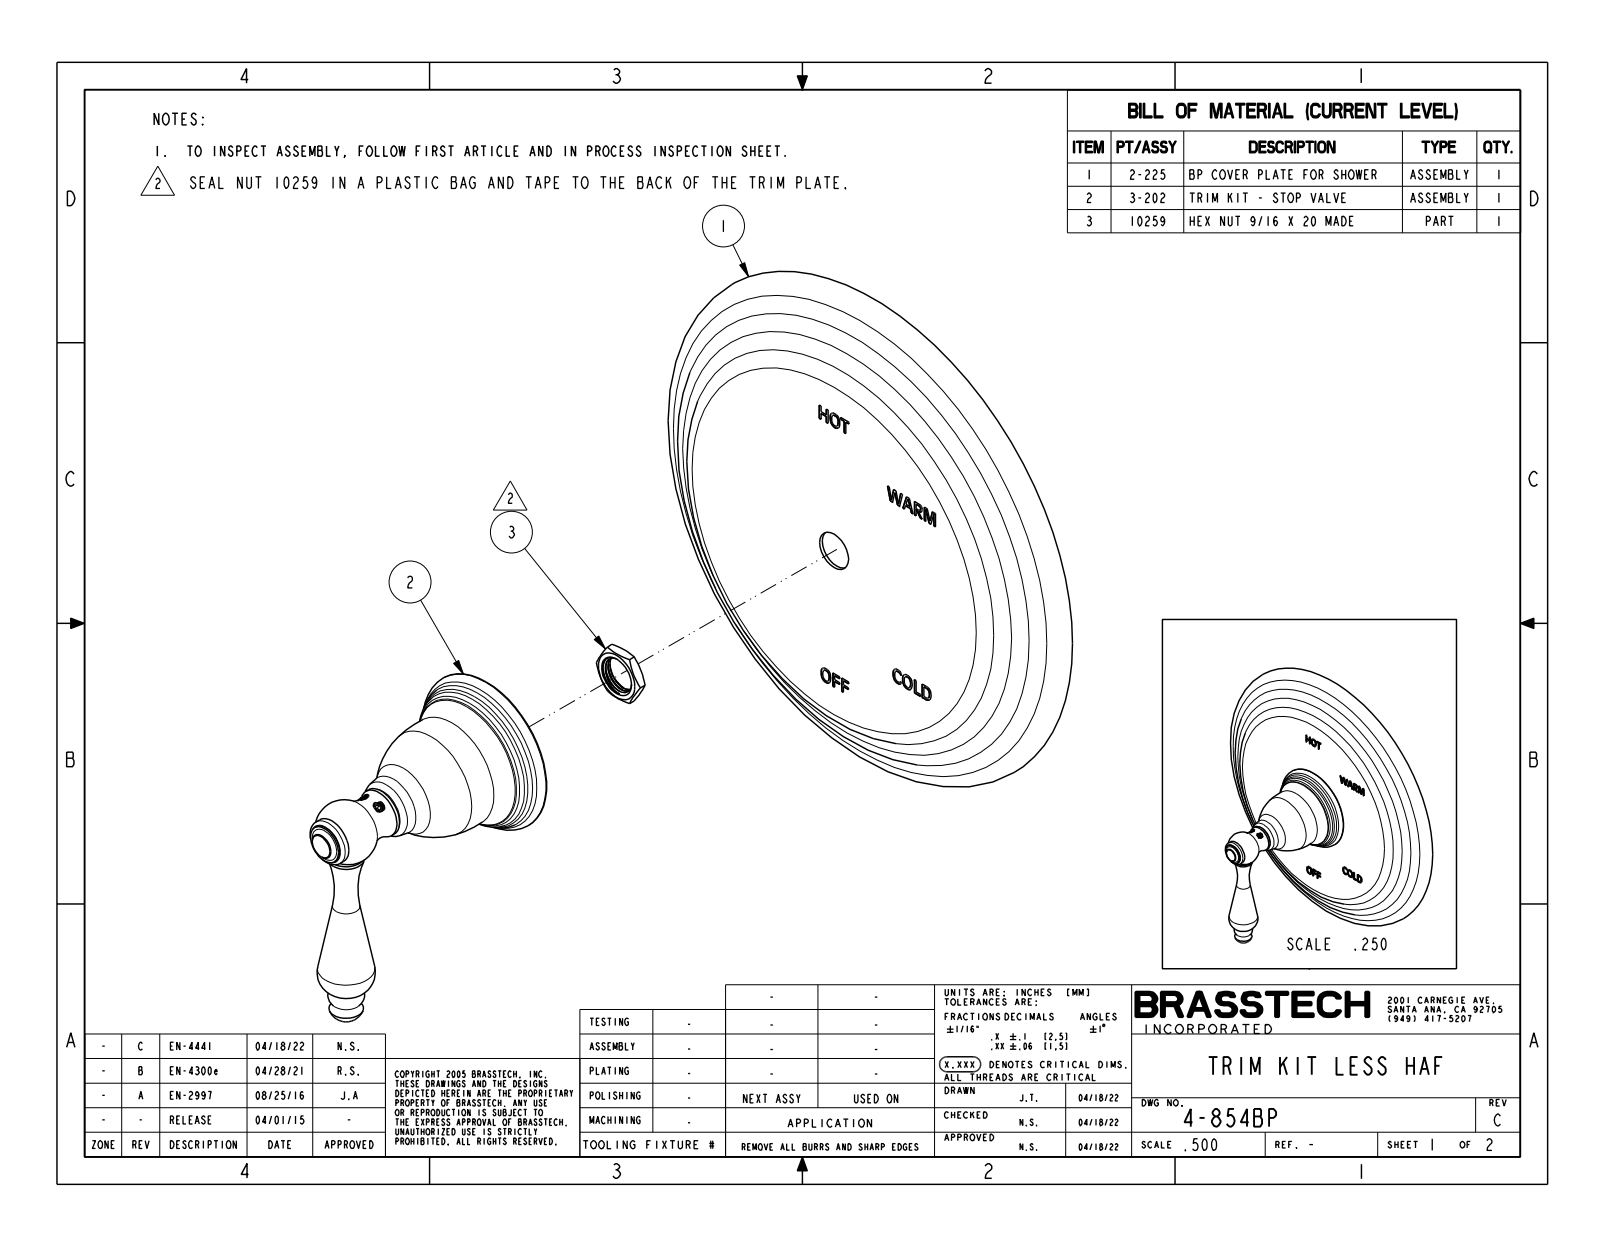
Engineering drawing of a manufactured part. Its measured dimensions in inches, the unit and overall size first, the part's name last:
Units: inches
Overall size (bounding box): 7.75 × 7.75 × 3.963
Round bosses / shafts (diameter × count): ⌀2.34 ×1, ⌀0.705 ×1, ⌀0.661 ×1, ⌀0.544 ×1, ⌀0.5 ×1, ⌀0.4 ×1
Main face-to-face distances: 0.754, 2.793, 2.039, 0.75, 2.043, 2.762, 2.011, 2.008, 0.031, 3.963
Volume: 32.67 in³ · Surface area: 116.2 in²
Bodies: 1 solid, 282 faces (130 planar, 12 cylindrical, 140 other)
Part name (STEP PRODUCT): 4-854BP
STEP written by: CREO PARAMETRIC BY PTC INC, 2018400 (CONFIG_CONTROL_DESIGN)
